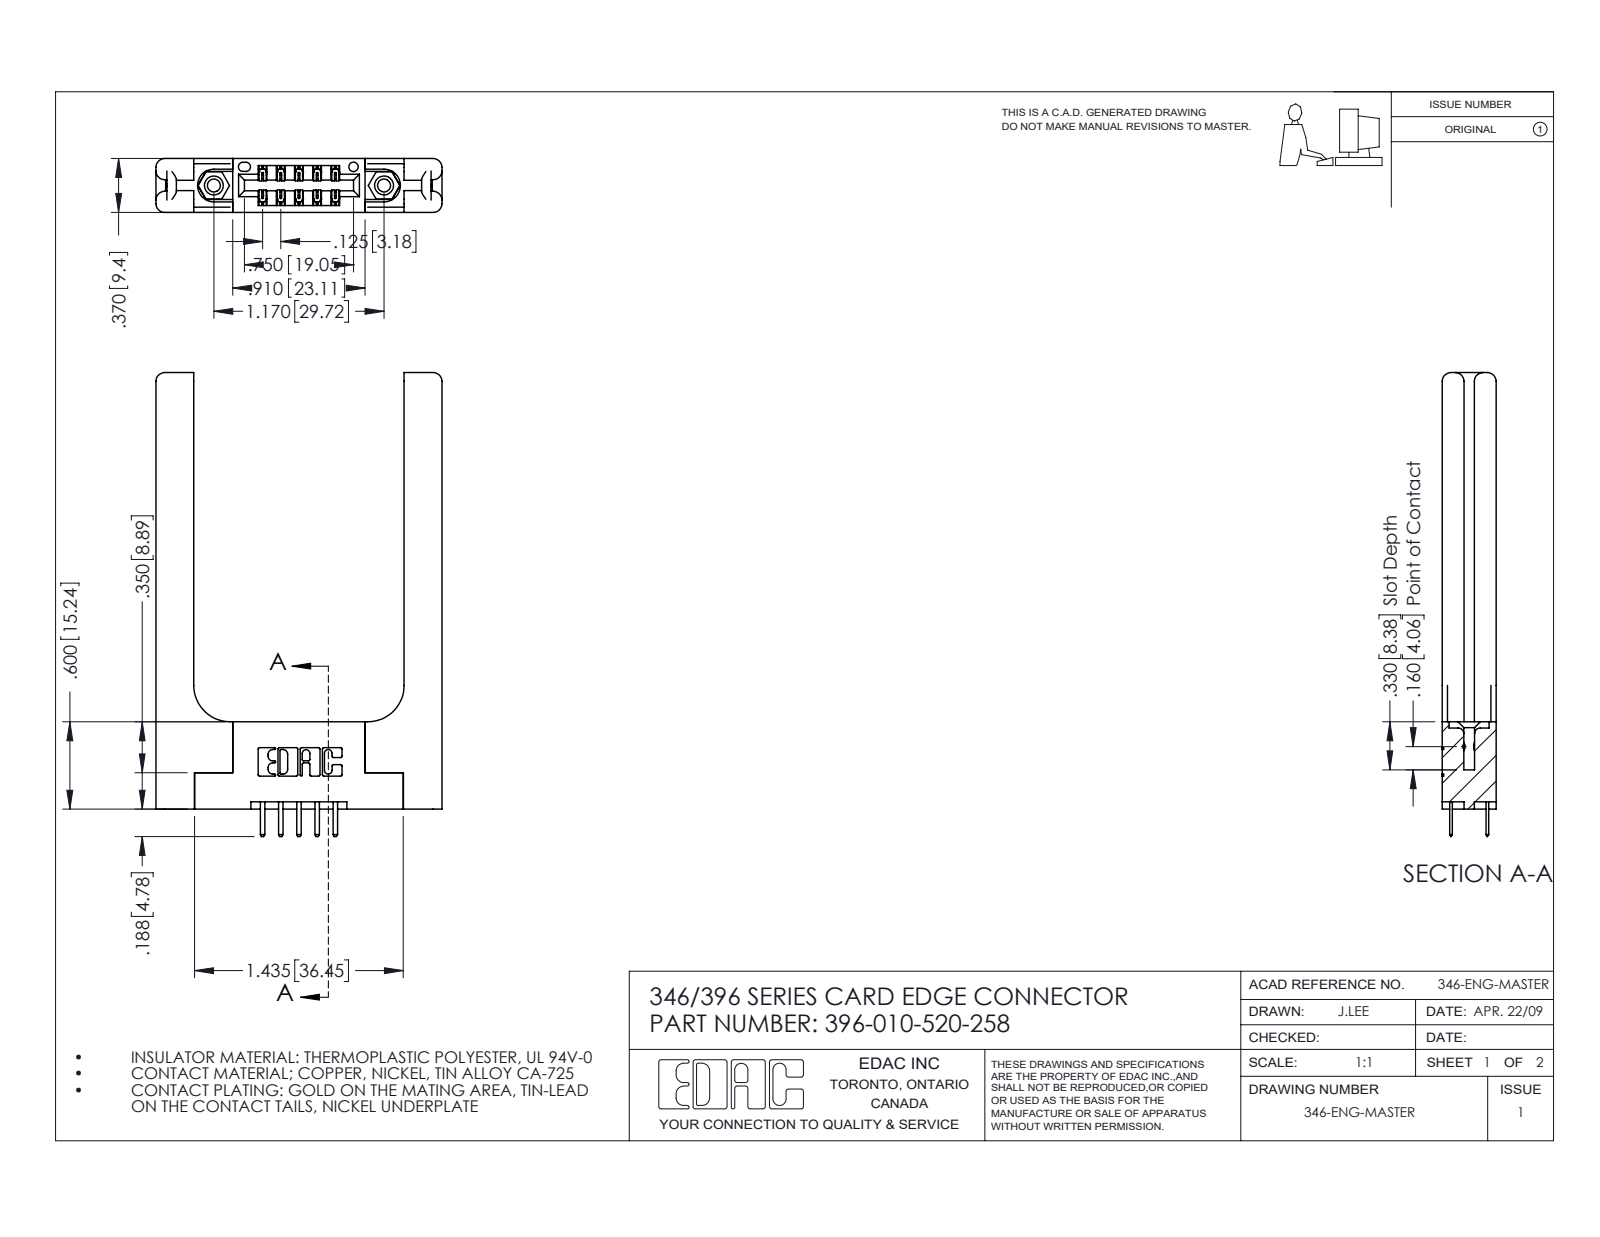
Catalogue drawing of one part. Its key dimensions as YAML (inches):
part_name: "345-292-001_345-293-120; 346 Part_Flush Mounting Lugs - 0.156 Dia-TH; 396-010-520-258; 345-250-001_345-250-001-102 (+1 more)"
step_written_by: "SolidWorks 2016 (CONFIG_CONTROL_DESIGN)"
units: inches
bodies: {solids: 15, faces: 938, planar: 594, cylindrical: 284, other: 60}
overall_size: [3.188, 1.966, 0.37]
volume: 0.737
surface_area: 16.54
round_holes:
  - {diameter: 0.089, count: 2}
  - {diameter: 0.125, count: 2}
  - {diameter: 0.156, count: 2}
  - {diameter: 0.064, count: 1}
round_bosses_or_shafts:
  - {diameter: 0.155, count: 2}
partial_cylinders:
  - {radius: 0.01, count: 22}
  - {radius: 0.06, count: 16}
  - {radius: 0.006, count: 15}
  - {radius: 0.01, count: 14}
  - {radius: 0.007, count: 6}
  - {radius: 0.031, count: 6}
  - {radius: 0.026, count: 3}
  - {radius: 0.014, count: 2}
face_to_face_distances: [0.37, 0.15, 0.22, 0.25, 0.072, 1.446, 0.148, 0.071, 0.26, 1.706]
hole_center_spacings: [0.246, 0.969, 1.17]
